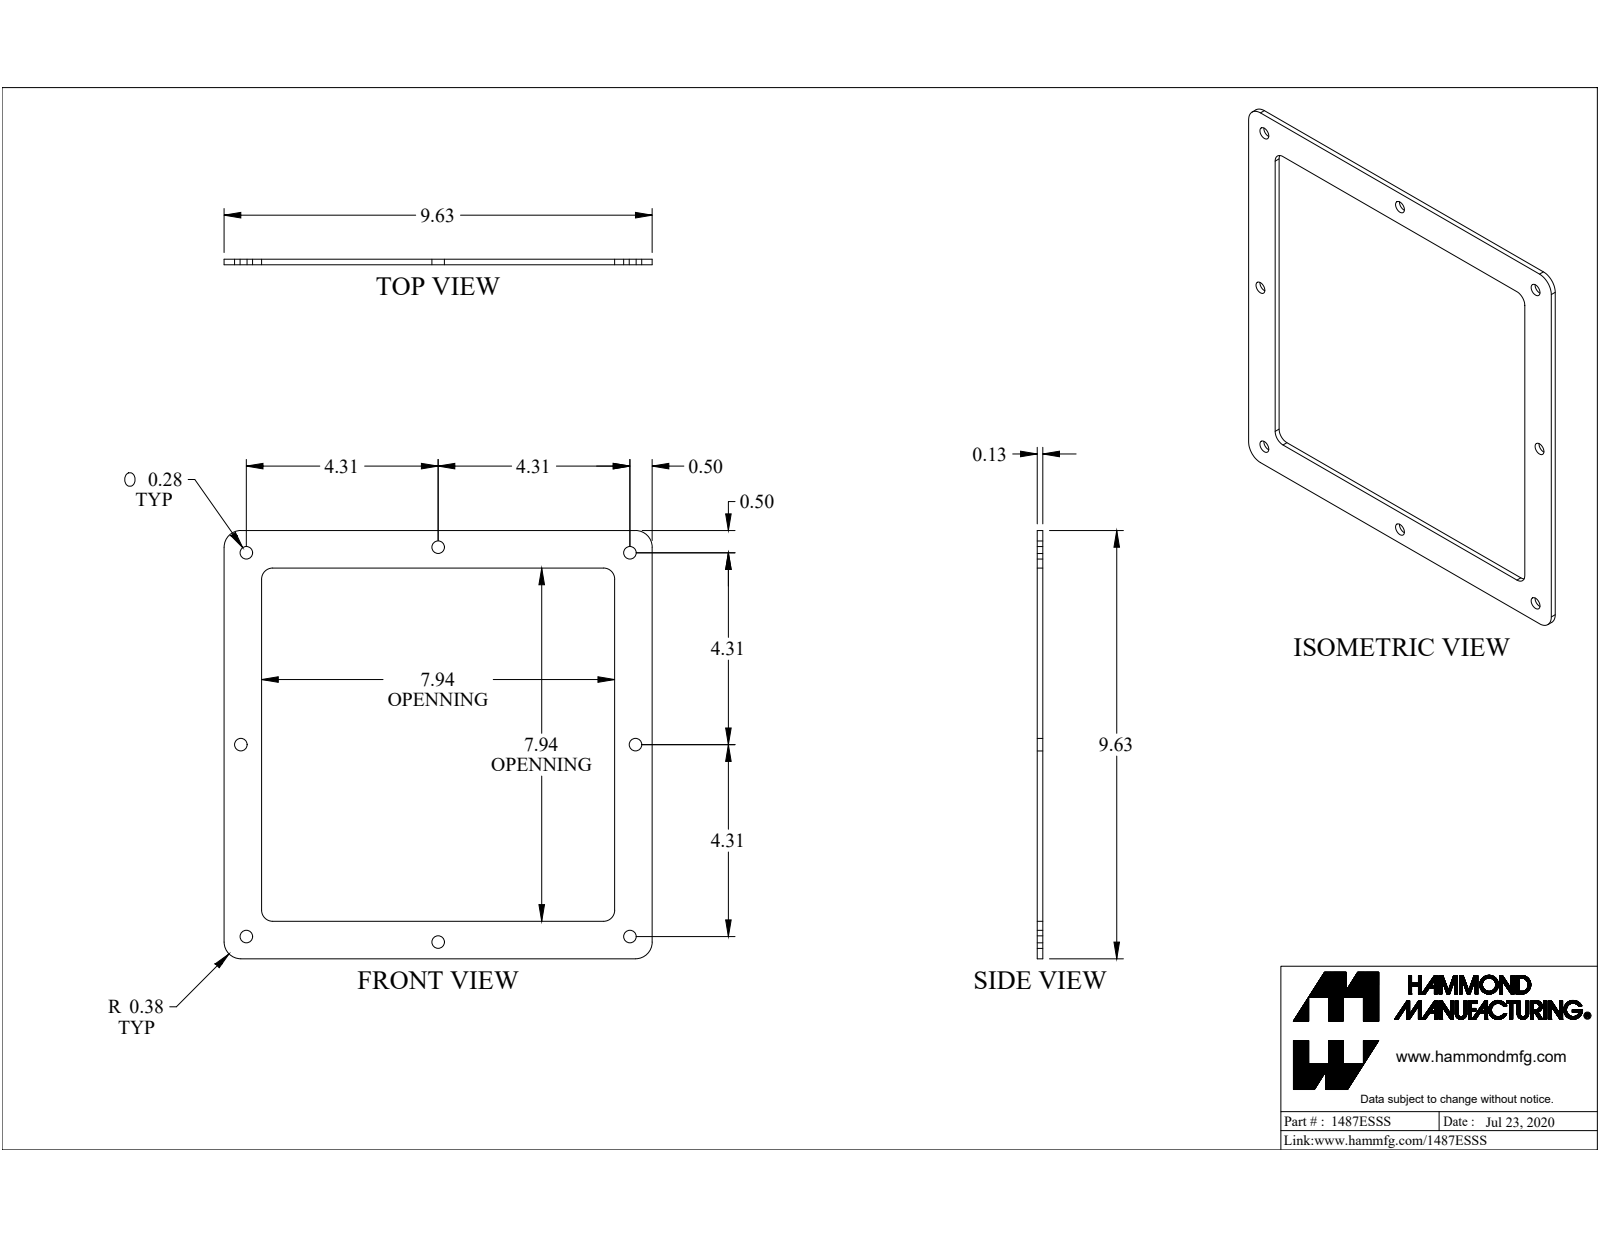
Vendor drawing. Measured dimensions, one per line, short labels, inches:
name: 1487ESSS
written by: SolidWorks 2019 (CONFIG_CONTROL_DESIGN)
unit: in
bodies: 1 solid, 26 faces (10 planar, 16 cylindrical, 0 other)
size: 9.625 × 9.625 × 0.125
volume: 3.631 in³; area: 67.63 in²
holes: 8× ⌀0.281
rounds: 4× R0.25, 4× R0.375
face distances: 0.125, 0.843, 8.782, 9.625, 7.939
hole spacings: 4.315, 9.755, 6.276, 8.625, 8.875, 12.198
